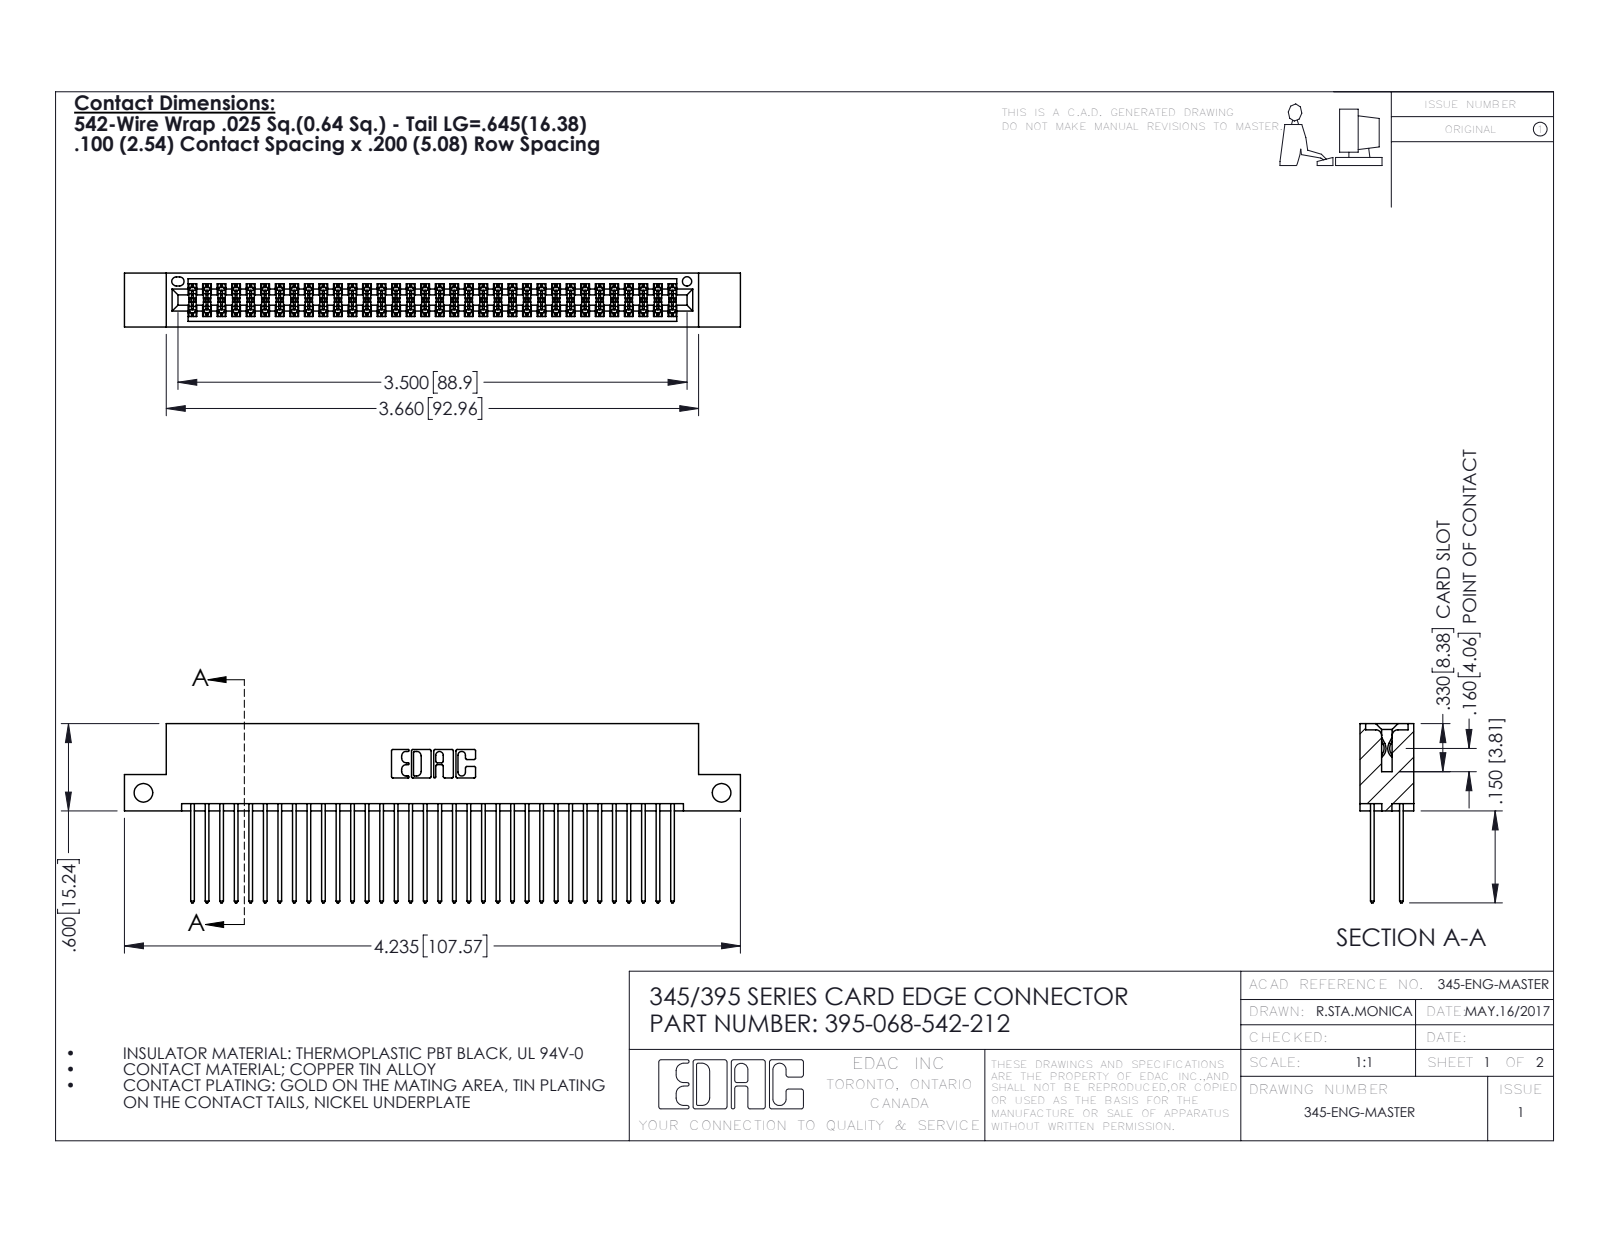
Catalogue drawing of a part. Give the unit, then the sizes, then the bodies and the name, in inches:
Units: inches
Overall size (bounding box): 4.235 × 1.232 × 0.37
Round holes (diameter × count): ⌀0.128 ×2, ⌀0.064 ×1
Partial cylindrical surfaces — rounded edges, fillets, slot ends (radius × count): R0.006 ×102, R0.01 ×68, R0.01 ×22, R0.007 ×6, R0.031 ×6, R0.026 ×3, R0.014 ×2, R0.019 ×2
Main face-to-face distances: 0.298, 0.072, 0.2, 0.098, 0.272, 0.025, 0.37, 0.225, 0.175, 0.149
Hole centre spacings: 3.975
Volume: 0.647 in³ · Surface area: 26.14 in²
Bodies: 69 solids, 3526 faces (2324 planar, 1202 cylindrical, 0 other)
Part name (STEP PRODUCT): 345 Part_Flush Mounting Lugs - Side Mount; 345-292-001_345-293-142; 395-068-542-212
STEP written by: SolidWorks 2016 (CONFIG_CONTROL_DESIGN)
